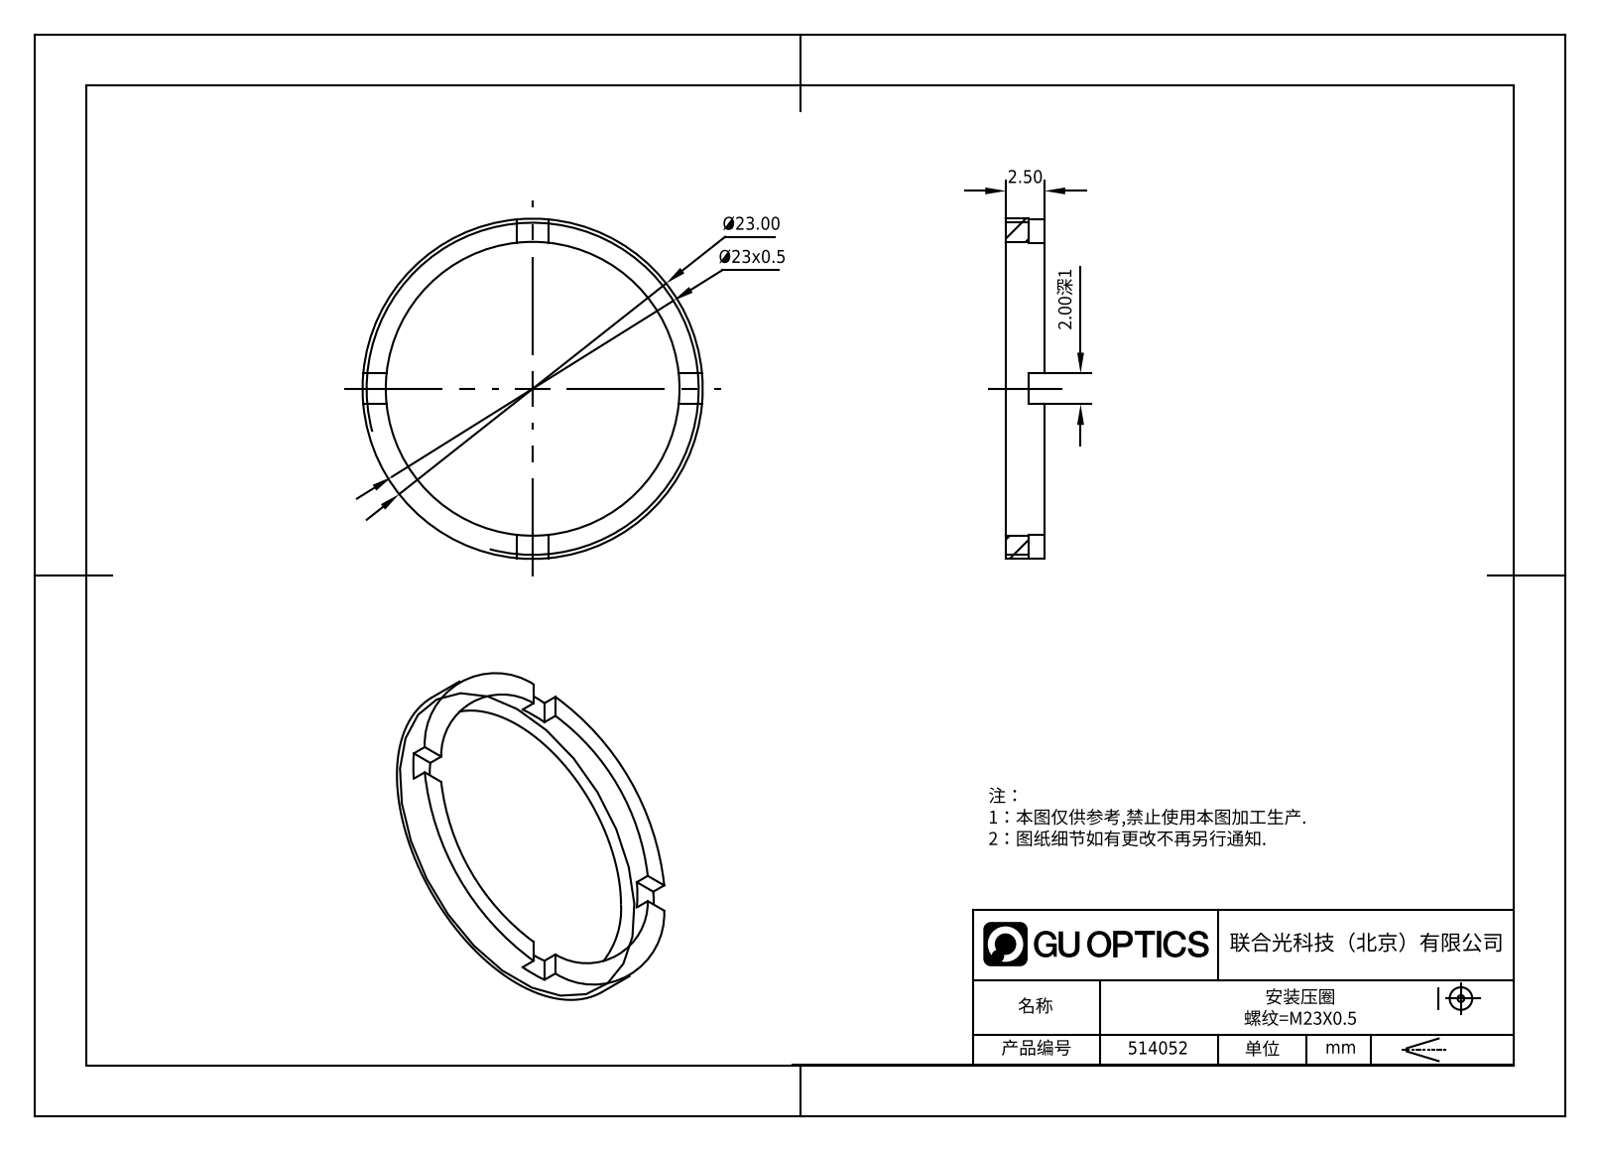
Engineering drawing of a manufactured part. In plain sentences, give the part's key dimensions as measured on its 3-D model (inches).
The part is named "514052". Its 3-D file was written by "SolidWorks 2020 (CONFIG_CONTROL_DESIGN)". It is 1 solid with 21 faces: 17 planar, 4 cylindrical and 0 other. Overall it measures 0.906 by 0.906 by 0.098 inches. Its volume is 0.015 cubic inches and its surface area 0.831 square inches. Round holes: 1 of diameter 0.787. Round bosses or shafts: 1 of diameter 0.906. The main face-to-face distances are 0.098, 0.059, 0.039, 0.079.
